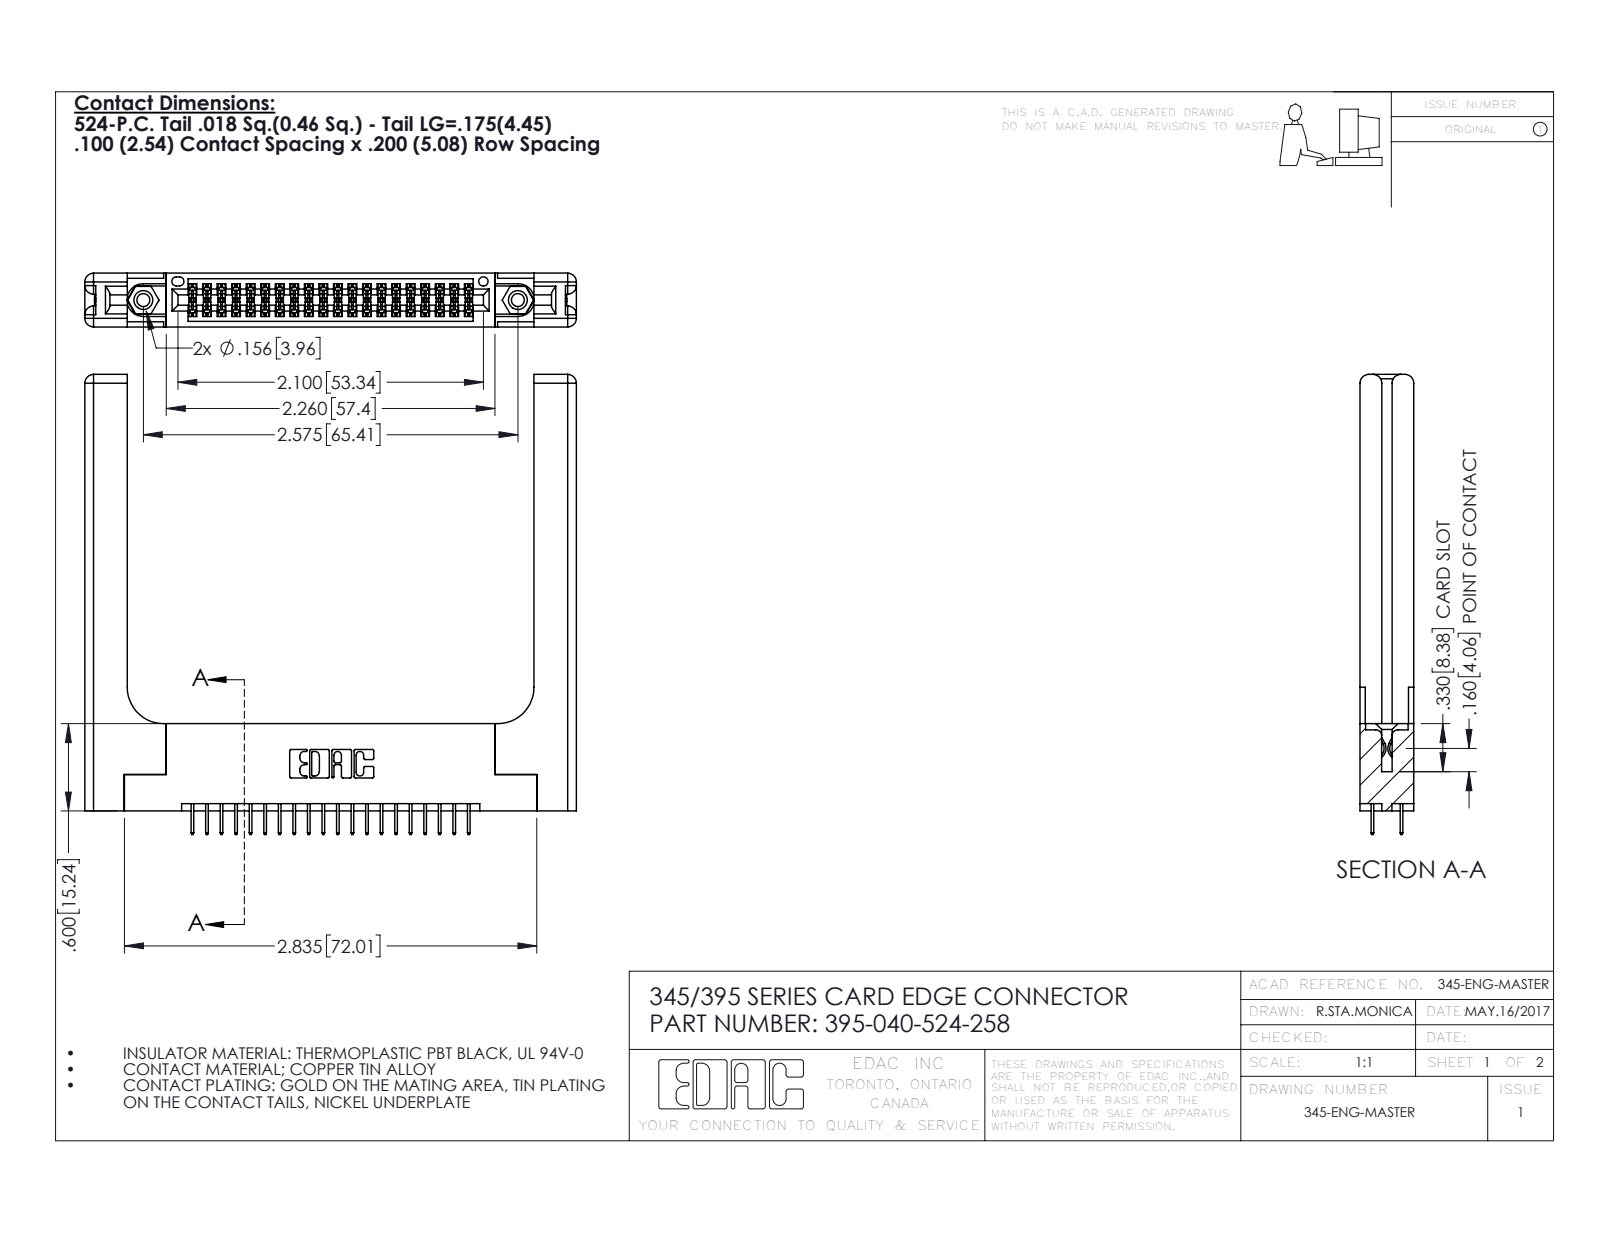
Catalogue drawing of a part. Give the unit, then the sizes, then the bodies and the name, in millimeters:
Units: millimetres
Overall size (bounding box): 85.8 × 80.3 × 9.4
Round holes (diameter × count): ⌀2.3 ×2, ⌀3.2 ×2, ⌀4 ×2, ⌀1.6 ×1
Round bosses / shafts (diameter × count): ⌀3.9 ×2
Partial cylindrical surfaces — rounded edges, fillets, slot ends (radius × count): R0.2 ×60, R0.3 ×22, R1.5 ×16, R0.2 ×6, R0.8 ×6, R0.7 ×3, R0.4 ×2, R0.5 ×2
Main face-to-face distances: 9.4, 1.8, 7.6, 5.1, 3.8, 3.8, 2, 5.6, 2.5, 6.9
Hole centre spacings: 6.9, 59.5, 65.4
Volume: 16 550 mm³ · Surface area: 16 410 mm²
Bodies: 45 solids, 2542 faces (1788 planar, 694 cylindrical, 60 other)
Part name (STEP PRODUCT): 345-220-058_345-220-058; 345 Part_Flush Mounting Lugs - 0.156 Dia-TH; 345-292-001_345-293-124; 345-250-001_345-250-001-102 (+1 more)
STEP written by: SolidWorks 2016 (CONFIG_CONTROL_DESIGN)
